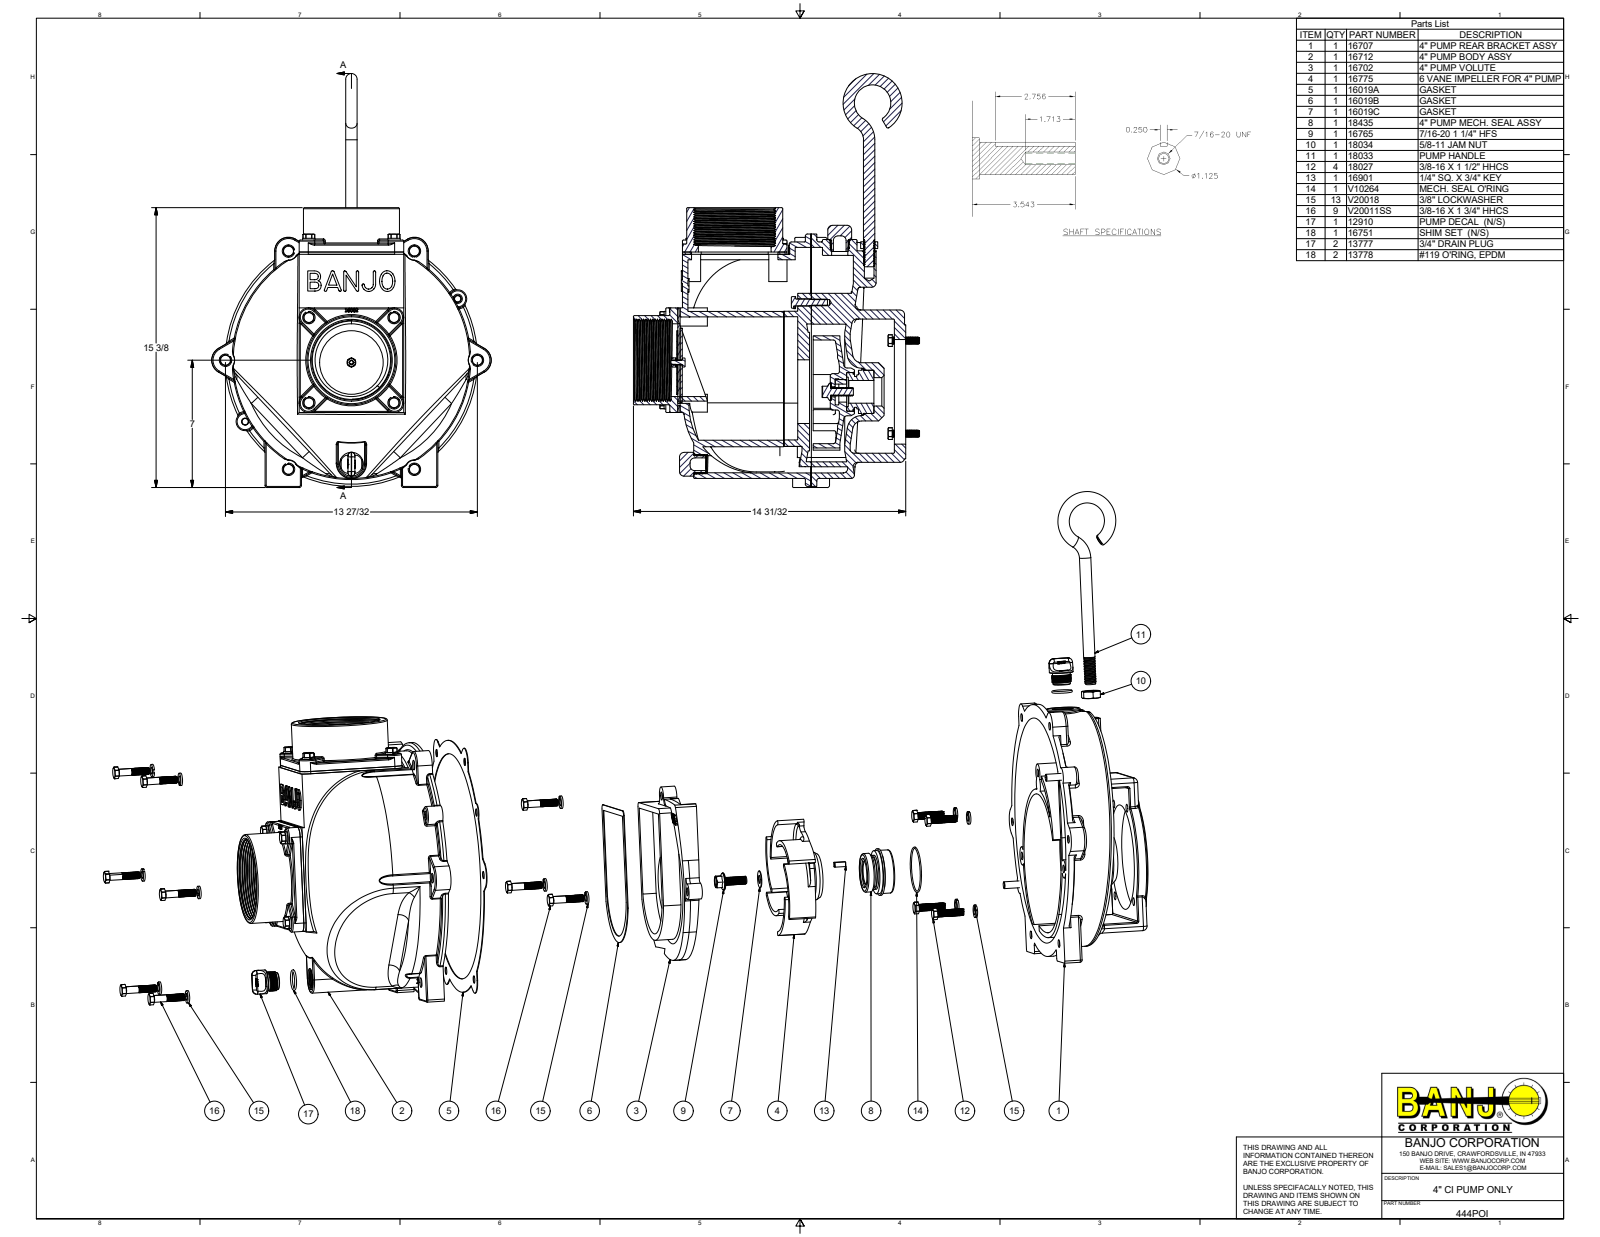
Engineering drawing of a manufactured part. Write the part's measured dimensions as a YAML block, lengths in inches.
part_name: "444POI; 16707; 16707X; 16020 (+8 more)"
step_written_by: "Autodesk Inventor 2018 (AUTOMOTIVE_DESIGN)"
units: inches
bodies: {solids: 70, faces: 6859, planar: 1128, cylindrical: 2665, other: 3066}
overall_size: [22.76, 15.738, 15.375]
volume: 415.5
surface_area: 2837
round_holes:
  - {diameter: 0.385, count: 21}
  - {diameter: 0.307, count: 17}
  - {diameter: 0.406, count: 16}
  - {diameter: 0.4, count: 8}
  - {diameter: 0.413, count: 6}
  - {diameter: 0.438, count: 4}
  - {diameter: 0.393, count: 3}
  - {diameter: 0.548, count: 3}
  - {diameter: 0.374, count: 2}
  - {diameter: 0.39, count: 2}
  - {diameter: 0.7, count: 2}
  - {diameter: 1.17, count: 2}
round_bosses_or_shafts:
  - {diameter: 0.324, count: 411}
  - {diameter: 0.375, count: 23}
  - {diameter: 0.687, count: 21}
  - {diameter: 0.212, count: 12}
  - {diameter: 1, count: 7}
  - {diameter: 4.5, count: 2}
  - {diameter: 1.31, count: 2}
  - {diameter: 13, count: 1}
partial_cylinders:
  - {radius: 0.06, count: 117}
  - {radius: 0.125, count: 59}
  - {radius: 0.162, count: 42}
  - {radius: 0.5, count: 28}
  - {radius: 0.25, count: 25}
  - {radius: 0.11, count: 12}
  - {radius: 0.322, count: 12}
  - {radius: 0.75, count: 10}
face_to_face_distances: [0.3, 0.031, 0.125, 7.346, 7.315, 7.221, 7.19, 5.05, 0.75, 0.5]
hole_center_spacings: [12.008, 6.928, 3.25, 3.312, 3.313, 3.826, 4.684, 4.685]
